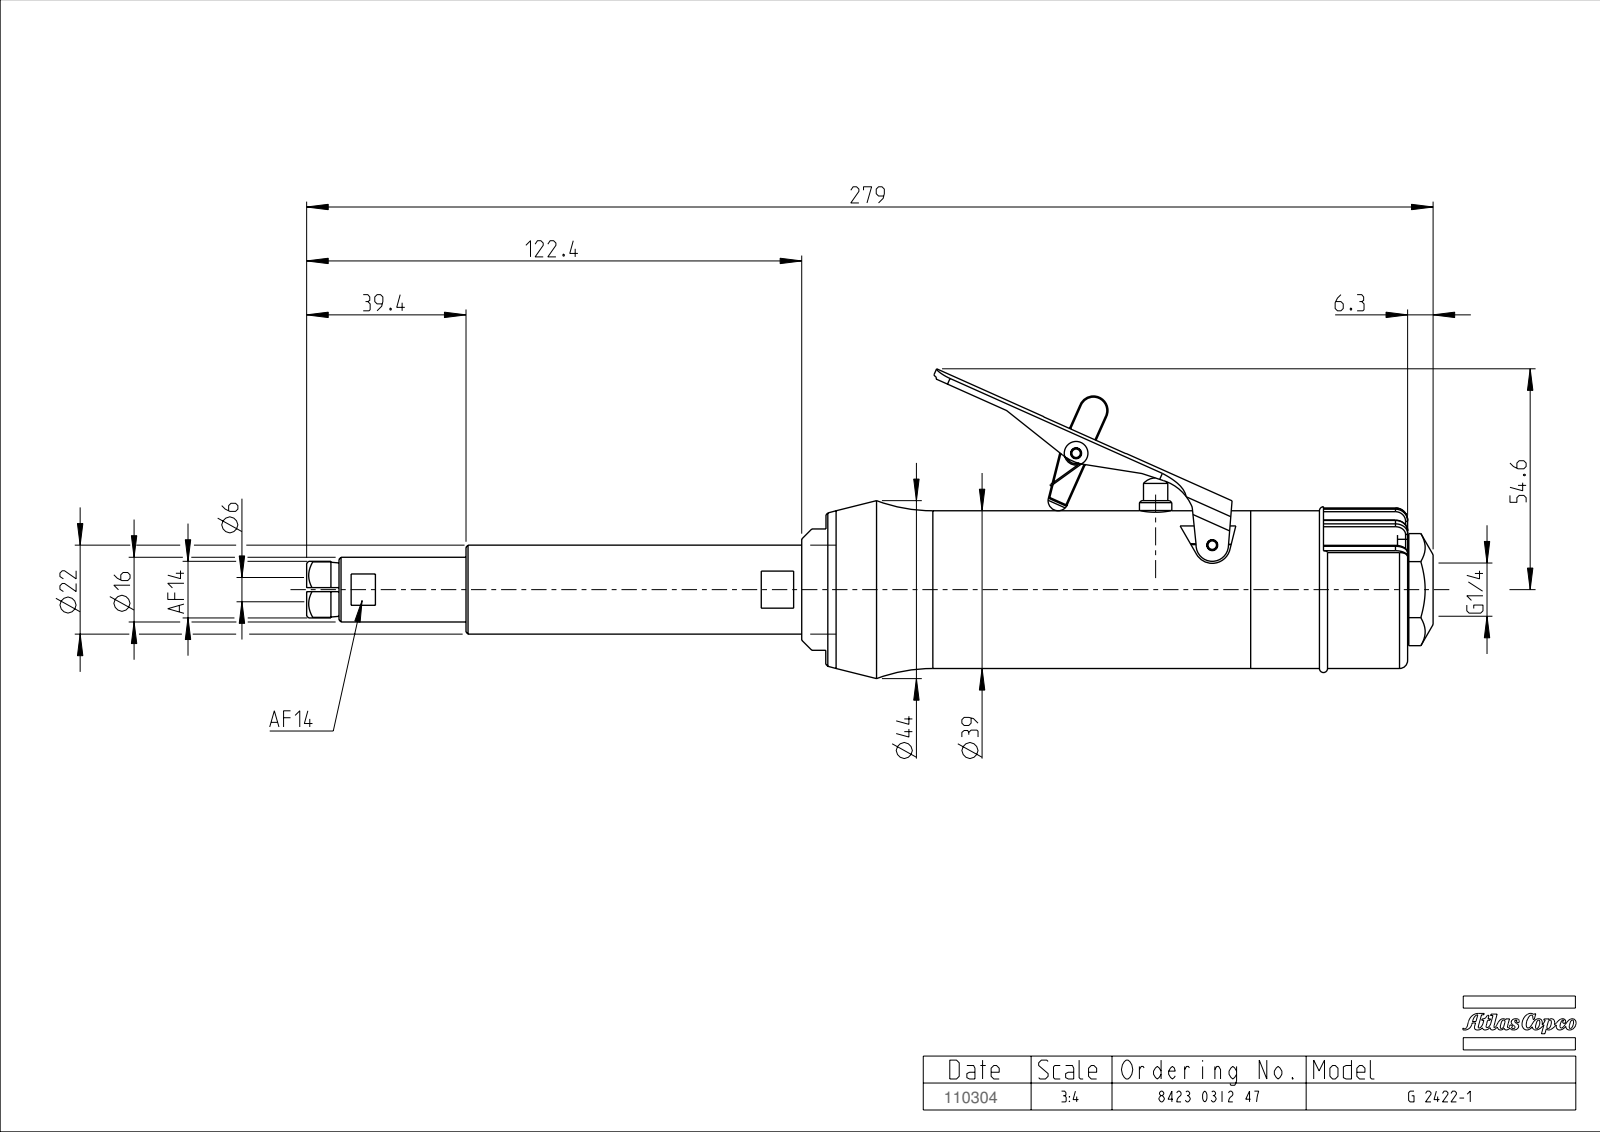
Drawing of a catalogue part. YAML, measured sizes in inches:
part_name: "TMP155518_SW"
step_written_by: "PRO/ENGINEER BY PARAMETRIC TECHNOLOGY CORPORATION, 2008310 (CONFIG_CONTROL_DESIGN)"
units: inches
bodies: {solids: 0, faces: 213, planar: 82, cylindrical: 73, other: 58}
overall_size: [10.965, 3.016, 1.732]
round_holes:
  - {diameter: 0.236, count: 1}
  - {diameter: 0.327, count: 1}
  - {diameter: 0.331, count: 1}
  - {diameter: 0.433, count: 1}
  - {diameter: 0.453, count: 1}
round_bosses_or_shafts:
  - {diameter: 1.535, count: 1}
  - {diameter: 1.496, count: 1}
  - {diameter: 0.866, count: 1}
  - {diameter: 0.63, count: 1}
  - {diameter: 0.236, count: 1}
partial_cylinders:
  - {radius: 0.02, count: 12}
  - {radius: 0.012, count: 6}
  - {radius: 0.157, count: 4}
  - {radius: 0.445, count: 2}
  - {radius: 0.451, count: 2}
  - {radius: 0.807, count: 2}
  - {radius: 0.007, count: 1}
  - {radius: 0.049, count: 1}
face_to_face_distances: [0.236, 0.118, 0.098, 0.295, 0.413, 0.866, 0.157, 0.177, 0.63, 0.945]
